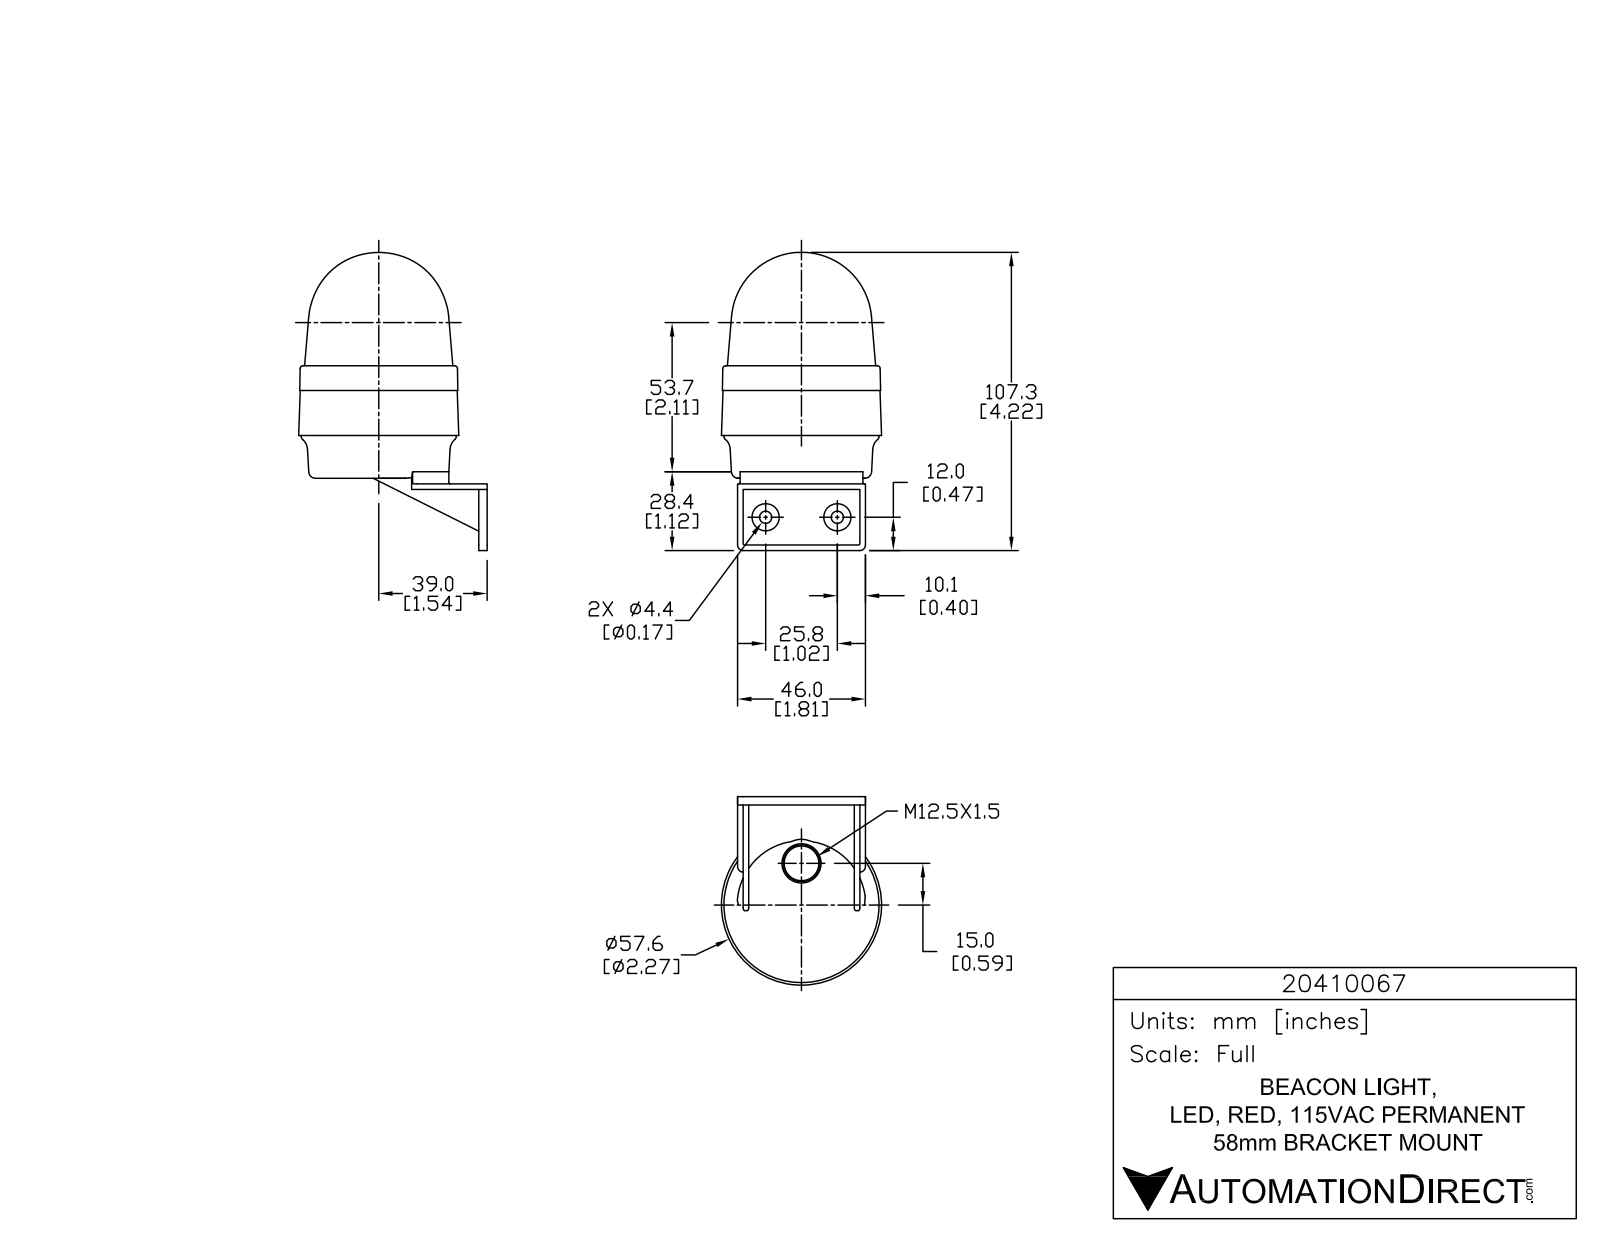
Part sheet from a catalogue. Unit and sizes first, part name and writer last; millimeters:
Units: millimetres
Overall size (bounding box): 107.3 × 72.4 × 61.1
Round holes (diameter × count): ⌀1 ×3, ⌀4.4 ×2
Round bosses / shafts (diameter × count): ⌀5.7 ×3, ⌀1.4 ×3, ⌀9.8 ×2, ⌀55.8 ×1
Partial cylindrical surfaces — rounded edges, fillets, slot ends (radius × count): R0.2 ×6, R0.2 ×6, R0.2 ×6, R0.5 ×6, R3.3 ×6, R2 ×4, R0.1 ×3, R0.1 ×3
Main face-to-face distances: 2, 4, 40, 42, 1, 3, 38, 22, 24, 19.4
Hole centre spacings: 25.8
Volume: 168 300 mm³ · Surface area: 21 540 mm²
Bodies: 1 solid, 828 faces (551 planar, 179 cylindrical, 98 other)
Part name (STEP PRODUCT): 20410067
STEP written by: SolidWorks 2015 (AUTOMOTIVE_DESIGN)
